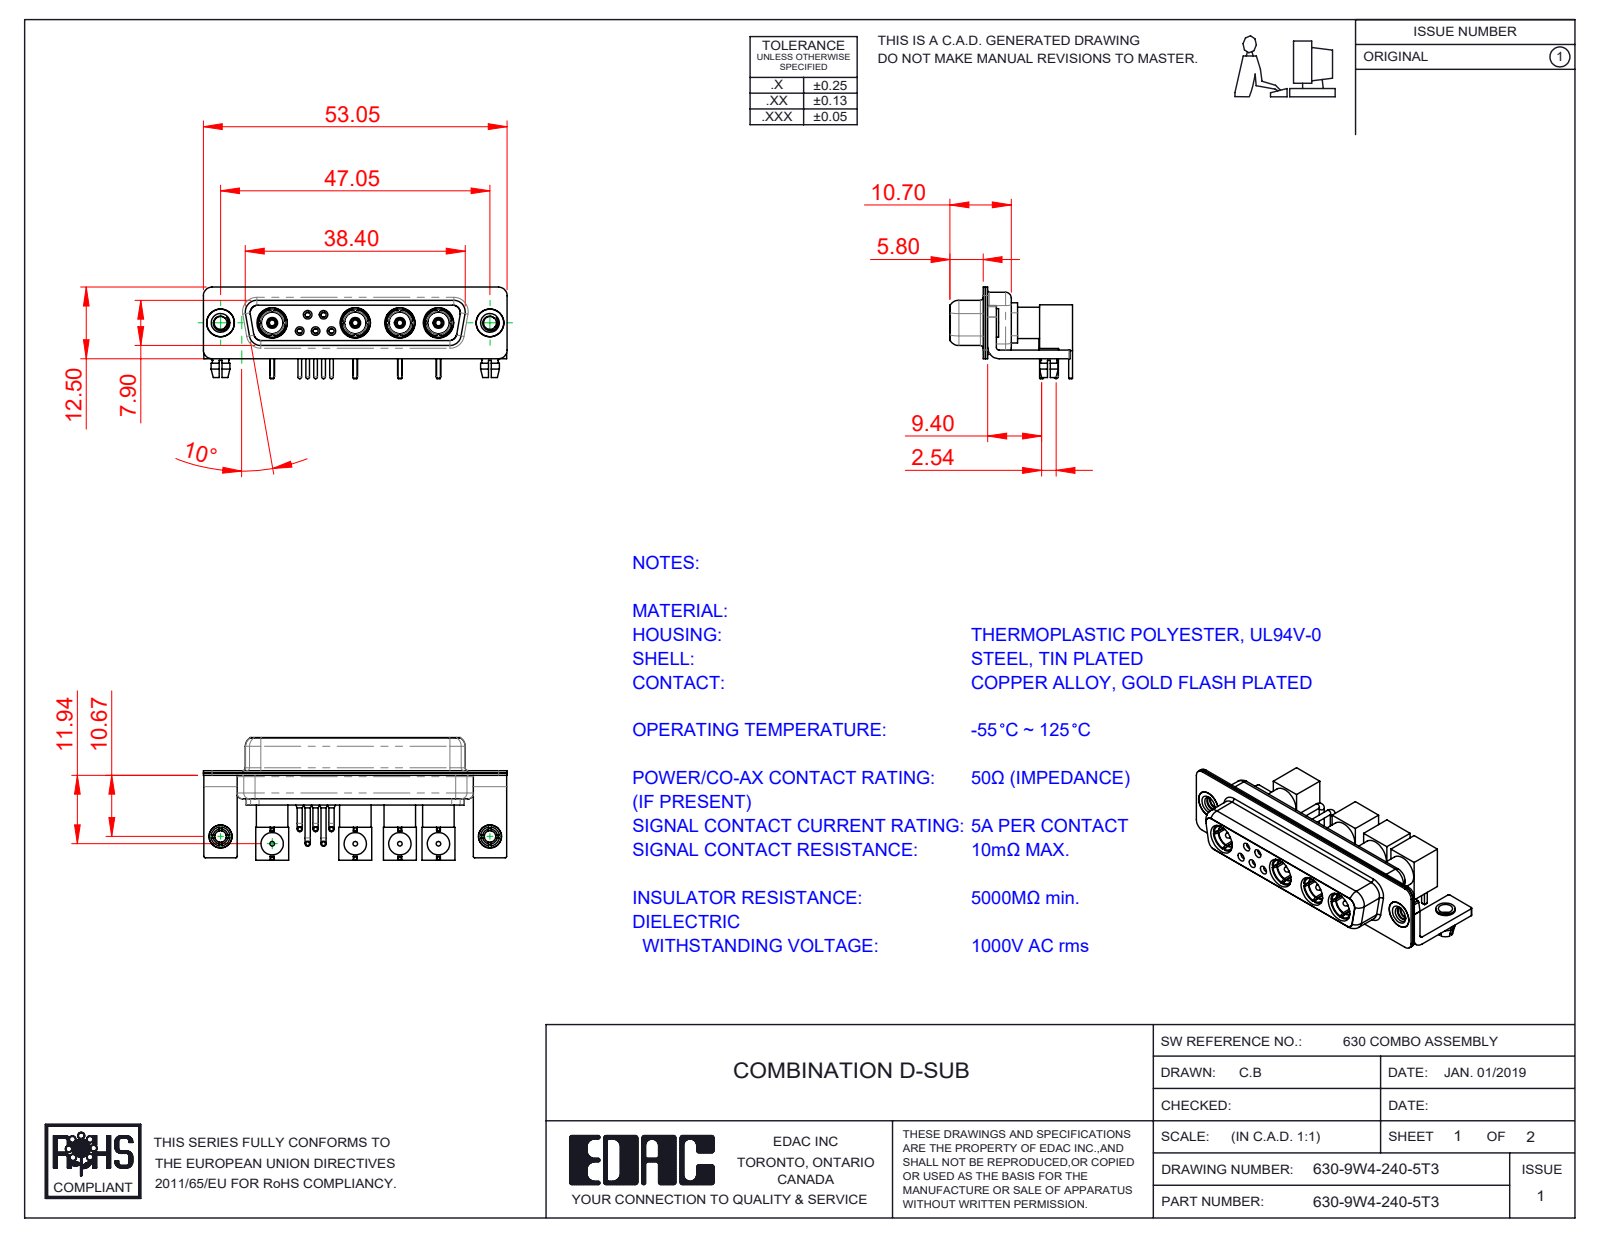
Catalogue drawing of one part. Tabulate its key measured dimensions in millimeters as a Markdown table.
| quantity | value |
| --- | --- |
| part name | 630Combo Shell Front_25 Contacts; Insulator Pin_Straight PC Tail; Co-Ax Plug Assy_RA; 630-9W4-240-5T3 (+8 more) |
| STEP written by | SolidWorks 2020 (CONFIG_CONTROL_DESIGN) |
| units | millimeters |
| bodies | 38 solids, 1348 faces (478 planar, 562 cylindrical, 308 other) |
| overall size | 53.05 × 21.41 × 16 |
| volume | 4 990 mm³ |
| surface area | 12 129 mm² |
| round holes (diameter × count) | 1.1 × 9, 1.5 × 9, 2 × 7, 4.85 × 6, 0.9 × 5, 0.8 × 4, 2.83 × 4, 3.1 × 4, 3.3 × 4, 3.9 × 4, 3.92 × 4, 4.1 × 4 |
| round bosses / shafts (diameter × count) | 5 × 6, 4 × 6, 2.9 × 6, 0.9 × 5, 0.8 × 5, 0.65 × 5, 5.5 × 4, 5.2 × 4 |
| partial cylindrical surfaces (radius × count) | 0.25 × 16, 1.5 × 16, 2 × 13, 1.35 × 8, 1.6 × 8, 0.5 × 5, 0.6 × 4, 0.65 × 4 |
| main face-to-face distances | 0.4, 1.4, 1.8, 0.45, 0.8, 8.45, 8.9, 1.35, 1.85, 7.05 |
| hole center spacings | 3.16, 6.74, 7.79, 14.51, 14.52, 14.53, 22.3, 29.04 |
